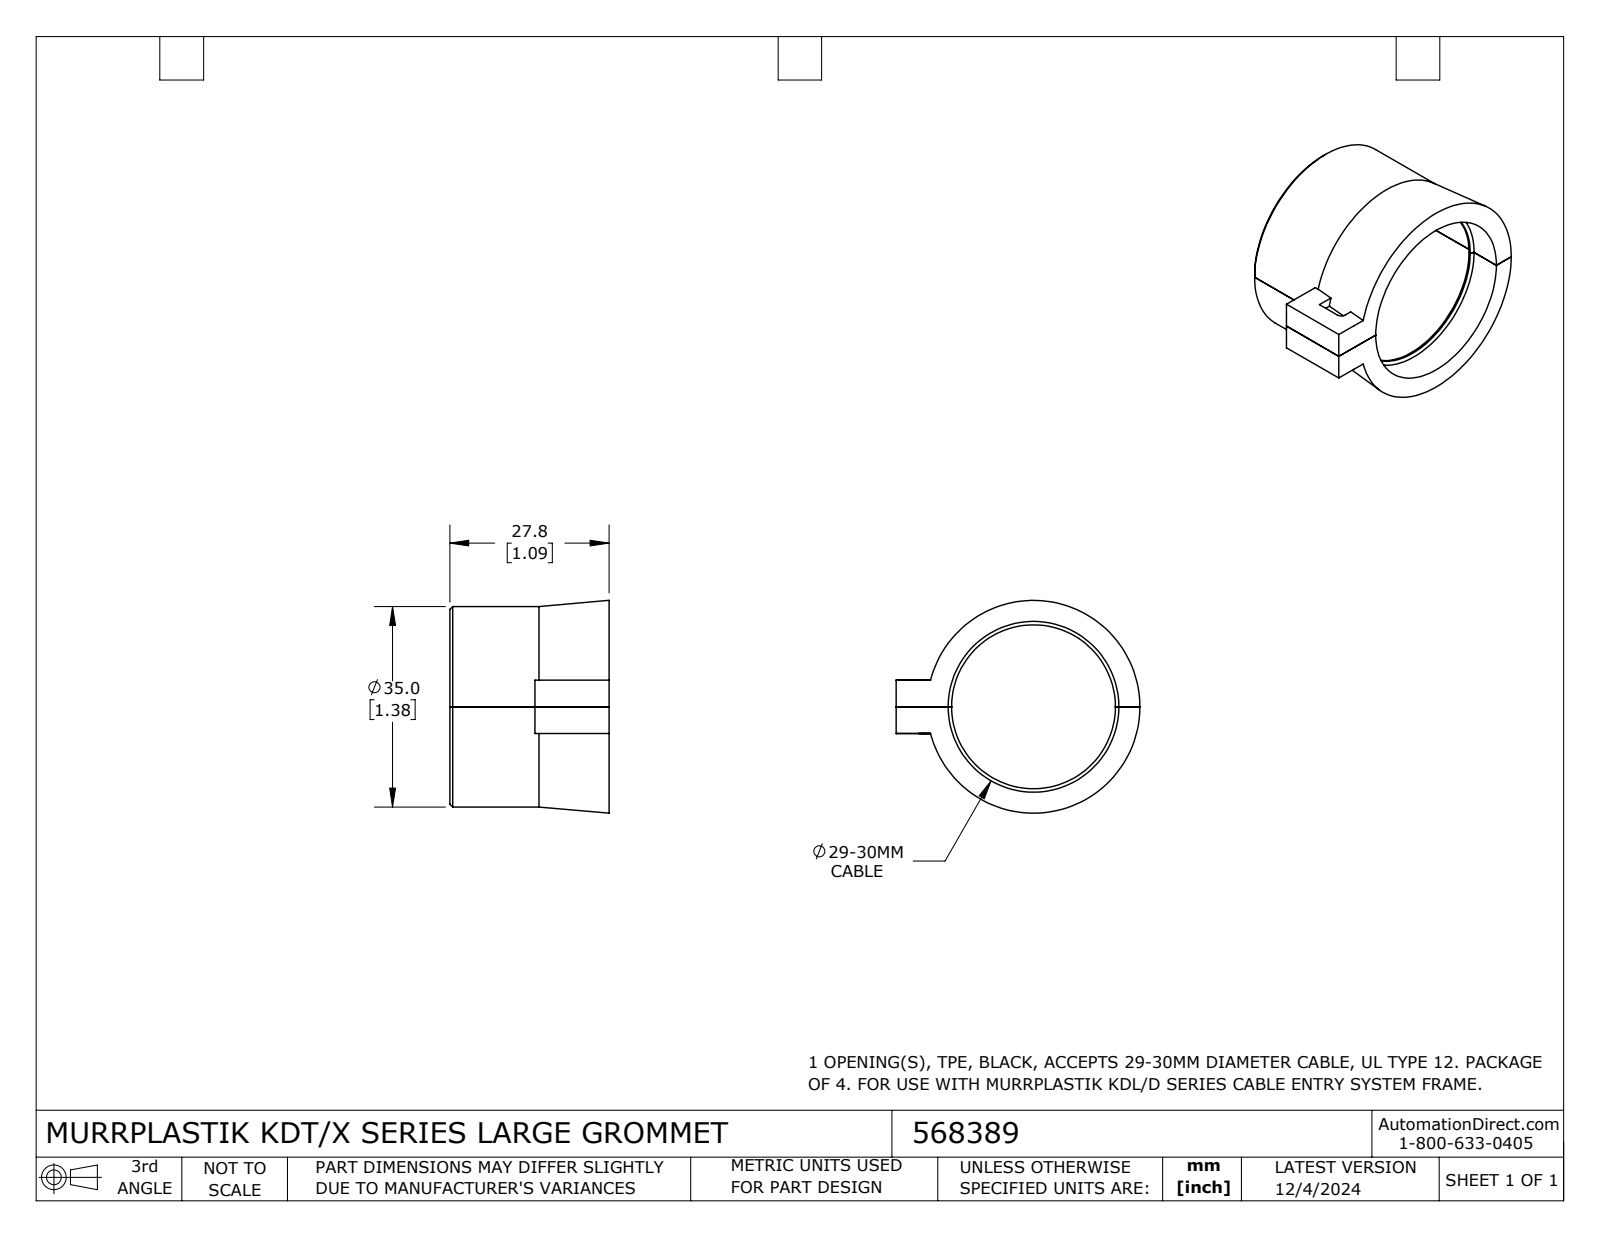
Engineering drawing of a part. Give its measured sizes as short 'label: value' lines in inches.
name: 568389
written by: SolidWorks 2024 (AUTOMOTIVE_DESIGN)
unit: in
bodies: 2 solids, 46 faces (22 planar, 14 cylindrical, 10 other)
size: 1.676 × 1.462 × 1.094
volume: 0.538 in³; area: 11.13 in²
holes: 1× ⌀1.126, 1× ⌀1.173
bosses: 1× ⌀1.378
rounds: 4× R0.02, 1× R0.039
face distances: 1.094, 0.183, 0.366, 0.51, 0.585, 0.061, 0.305, 0.122, 0.157, 0.243
